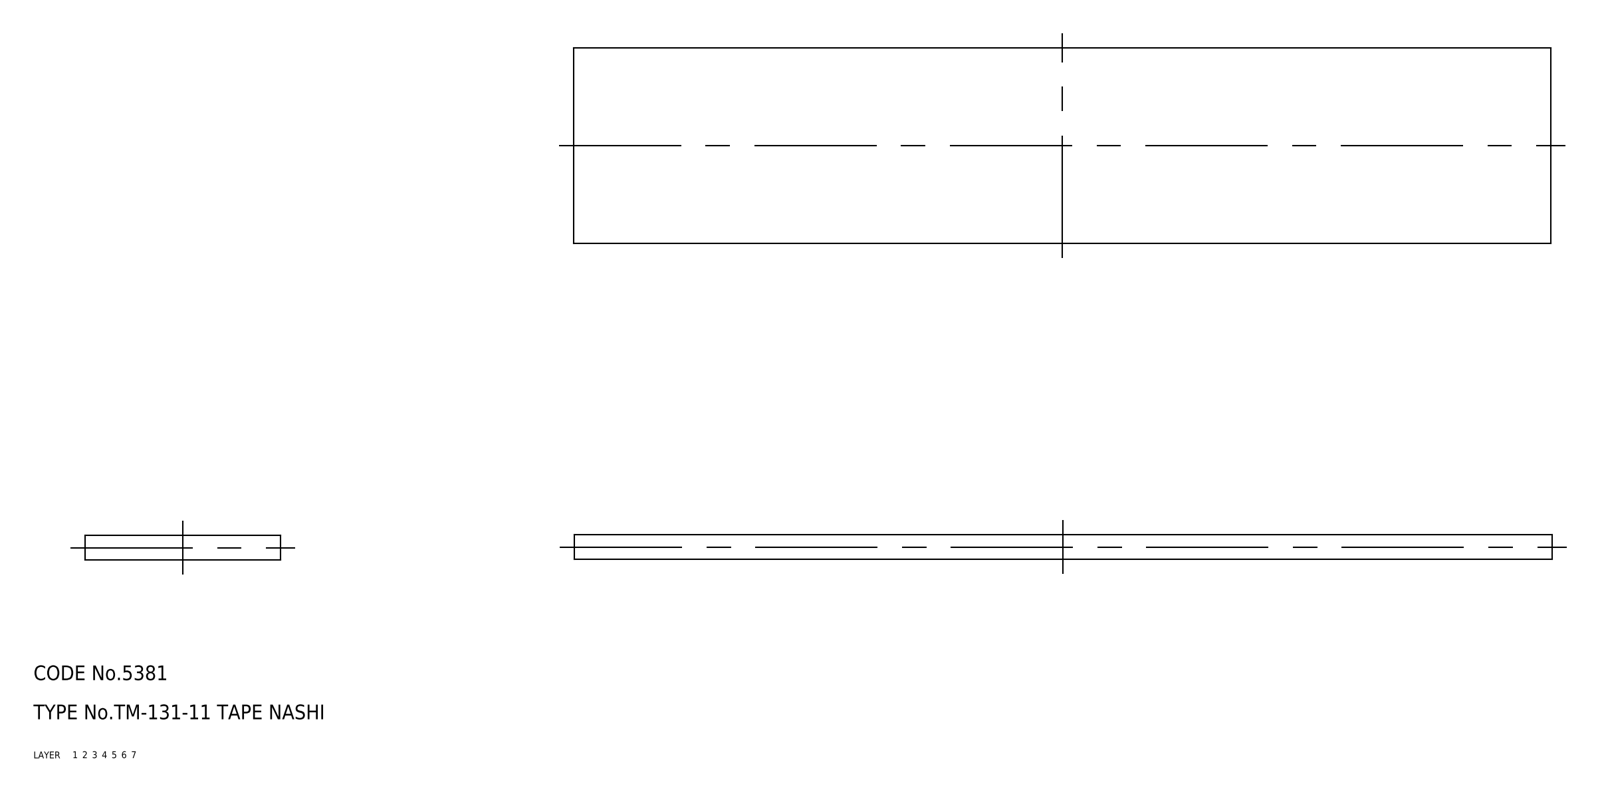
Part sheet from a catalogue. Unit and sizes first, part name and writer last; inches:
Units: inches
Overall size (bounding box): 7.874 × 1.575 × 0.197
Volume: 2.441 in³ · Surface area: 28.52 in²
Bodies: 1 solid, 6 faces (0 planar, 0 cylindrical, 6 other)
Part name (STEP PRODUCT): rubber foam
STEP written by: CADfix (AUTOMOTIVE_DESIGN)
